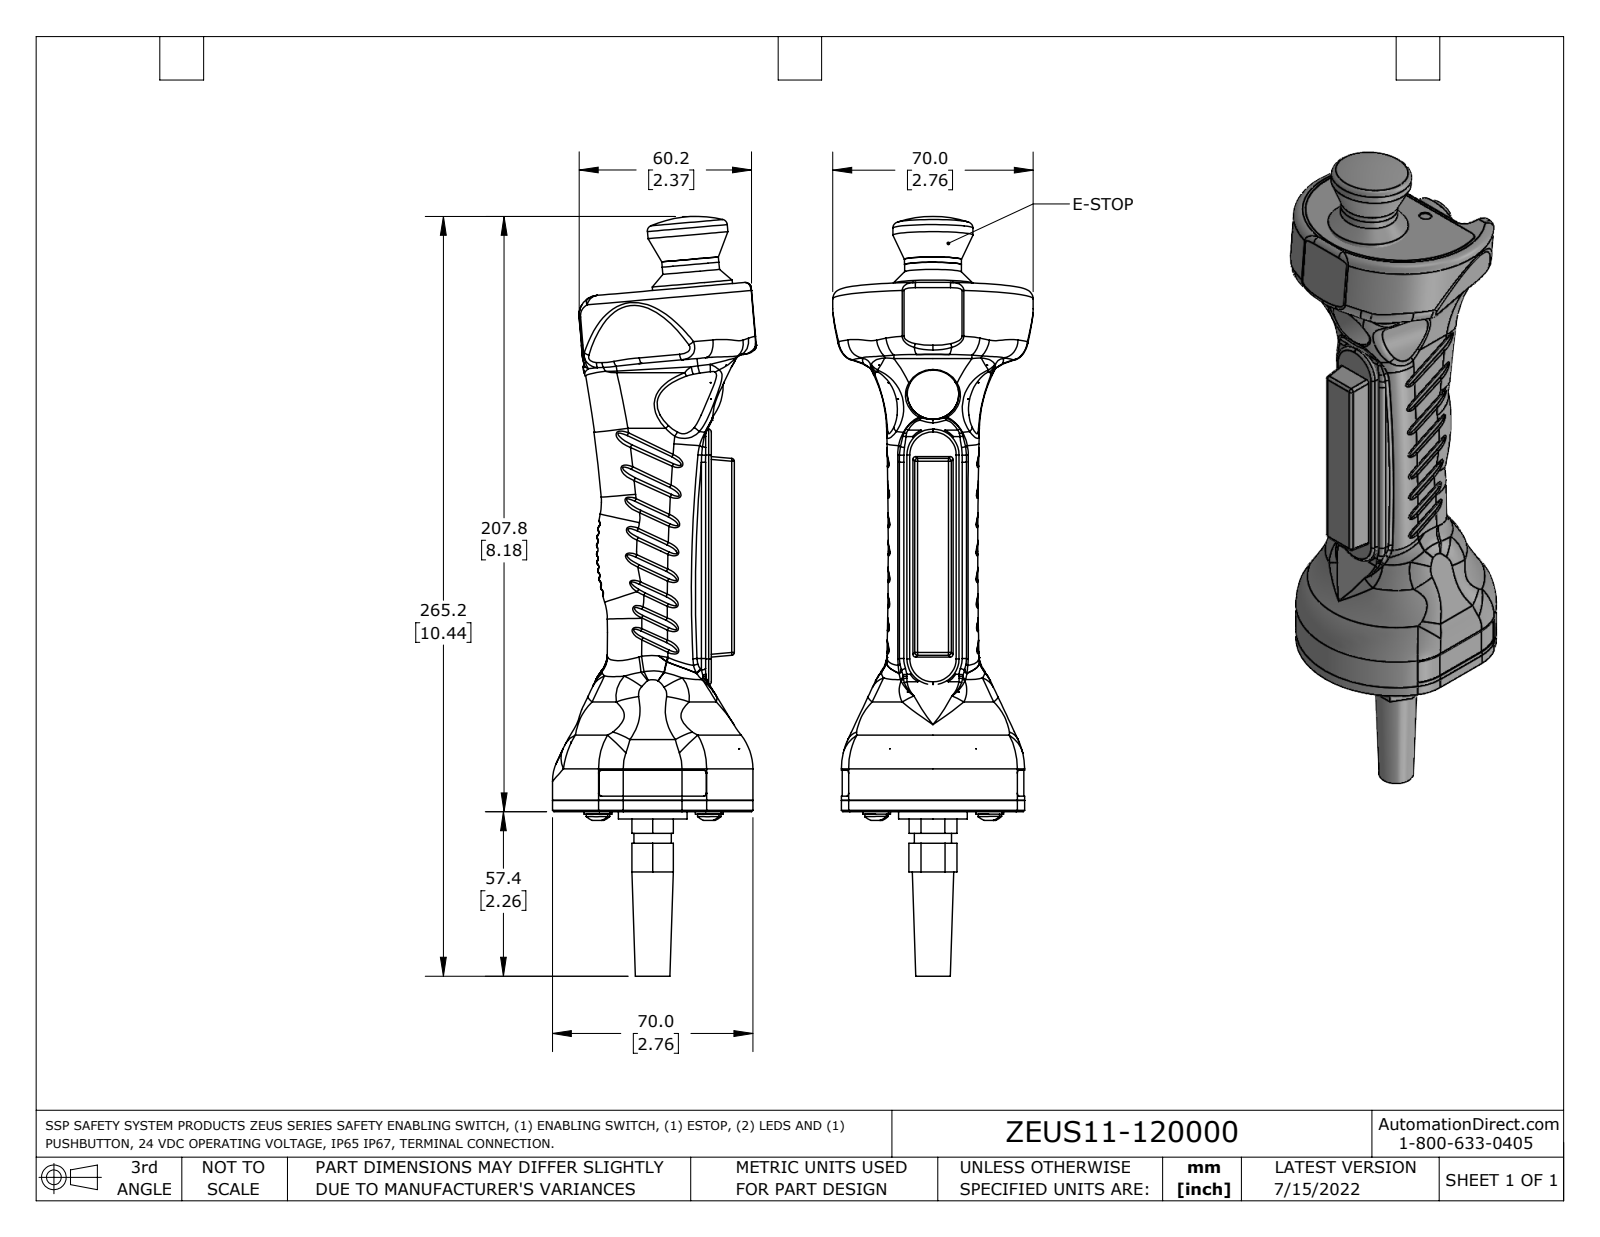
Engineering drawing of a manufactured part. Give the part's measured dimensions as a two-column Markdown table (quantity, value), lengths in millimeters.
| quantity | value |
| --- | --- |
| part name | ZEUS11-120000 |
| STEP written by | SolidWorks 2021 (AUTOMOTIVE_DESIGN) |
| units | millimeters |
| bodies | 21 solids, 1384 faces (477 planar, 459 cylindrical, 448 other) |
| overall size | 265.2 × 71.2 × 70 |
| volume | 397 700 mm³ |
| surface area | 83 350 mm² |
| round holes (diameter × count) | 3.4 × 4, 4.3 × 4, 4.5 × 4, 5 × 4, 2.5 × 2, 2.8 × 2, 4.2 × 2, 4.4 × 2, 8.4 × 2, 1 × 1, 4 × 1, 5.1 × 1 |
| round bosses / shafts (diameter × count) | 9 × 4, 7.5 × 4, 4 × 4, 1 × 4, 28 × 2, 19.8 × 2, 11.7 × 2, 6 × 2 |
| partial cylindrical surfaces (radius × count) | 0.1 × 96, 1 × 51, 0.7 × 48, 0.2 × 22, 2 × 21, 3 × 10, 0.2 × 8, 0.8 × 7 |
| main face-to-face distances | 4, 2, 0.5, 0.4, 1.7, 1.5, 2.5, 1, 4.5, 14.5 |
| hole center spacings | 10.3, 16, 22, 27.4, 30, 38.9, 39.6, 13 |
